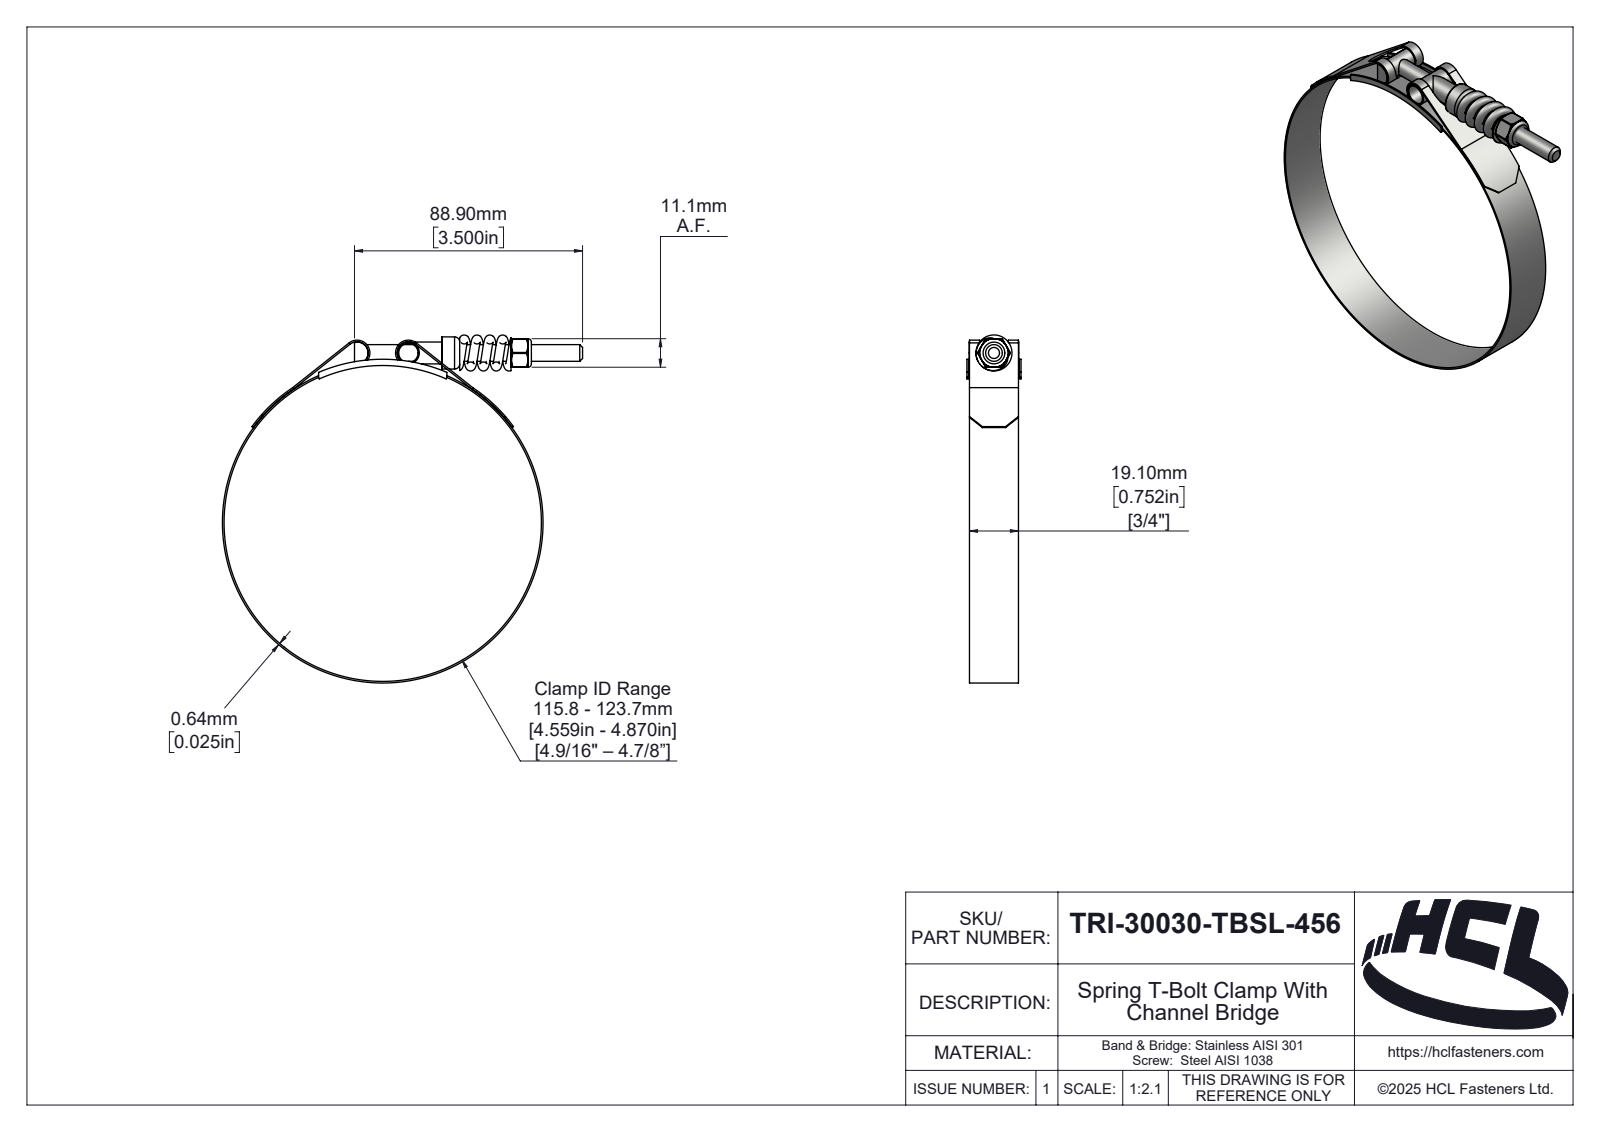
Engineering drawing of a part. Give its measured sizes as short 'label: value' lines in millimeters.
name: TRI-30030-TBSL-456
written by: SolidWorks 2025 (AUTOMOTIVE_DESIGN)
unit: mm
bodies: 7 solids, 332 faces (48 planar, 122 cylindrical, 162 other)
size: 141.39 × 135.61 × 21.1
volume: 13 052 mm³; area: 28 096 mm²
holes: 1× ⌀5.4, 1× ⌀6.35, 1× ⌀6.5, 1× ⌀7.52, 1× ⌀123.7
bosses: 2× ⌀8.52, 1× ⌀124.98, 1× ⌀12.52
rounds: 6× R0.39, 2× R0.5, 2× R4.36, 2× R5, 1× R0.59, 1× R2.42, 1× R3.03, 1× R3.19
face distances: 0.64, 19.1, 1, 20.1, 20.46, 0.36, 19.46, 21.1, 61, 0.9
hole spacings: 66.85
